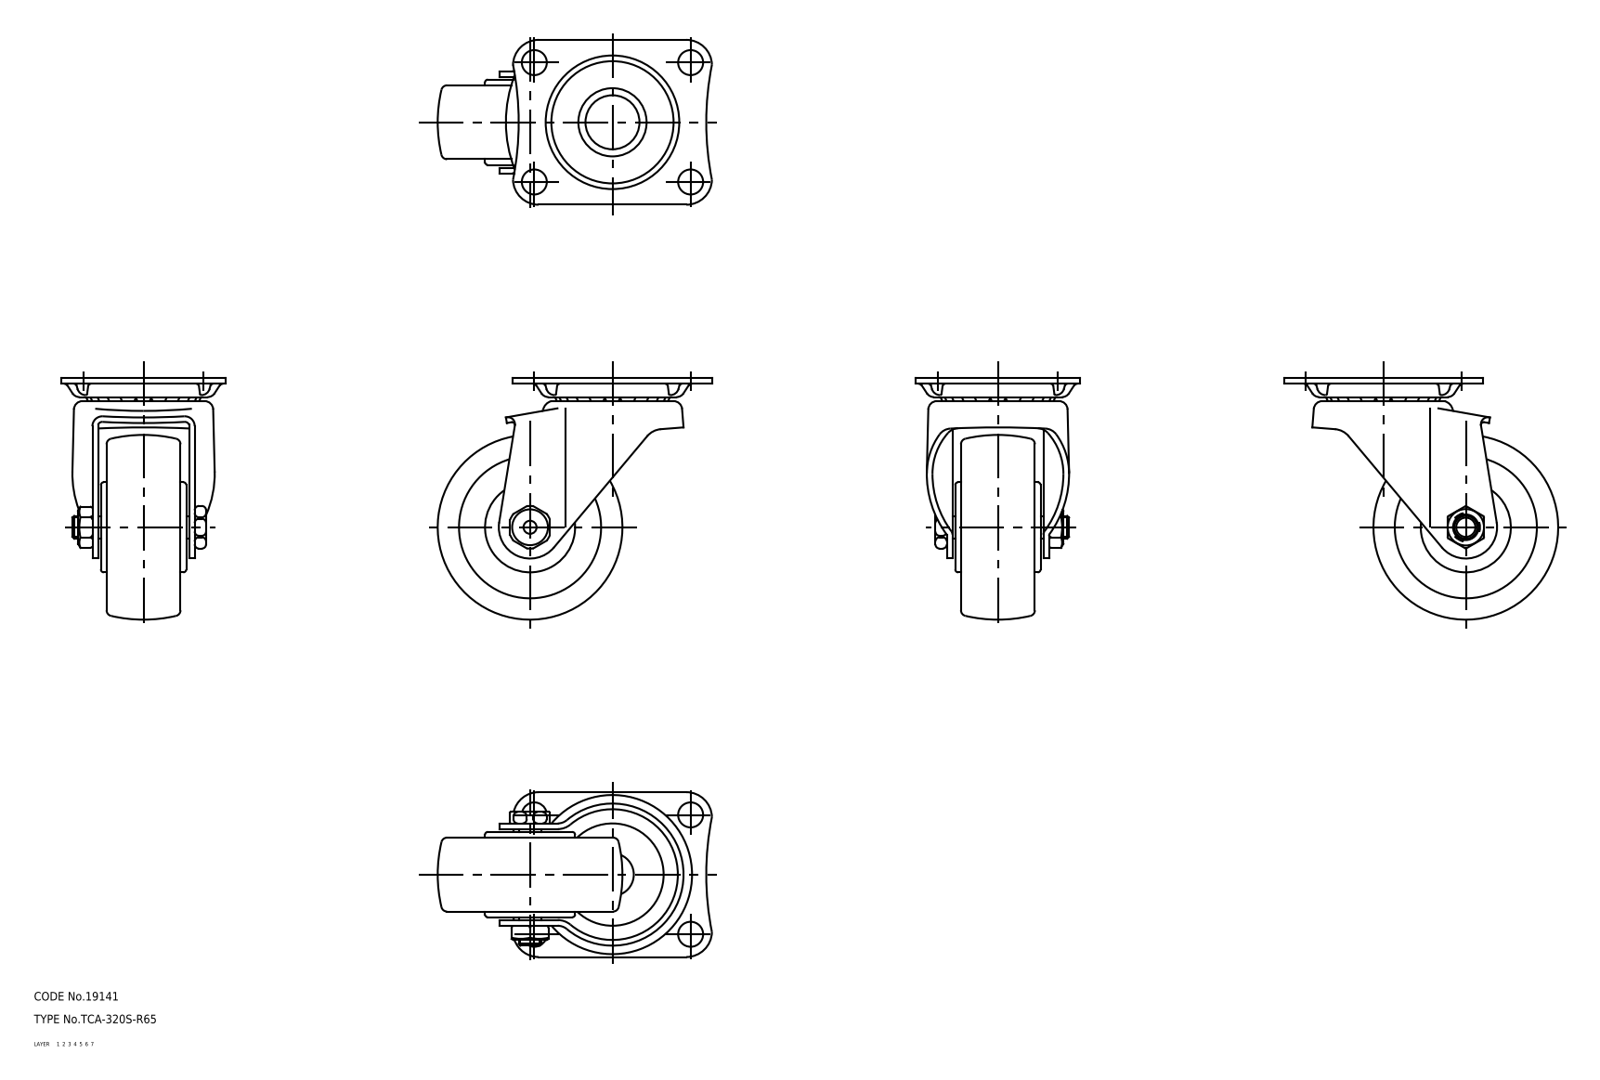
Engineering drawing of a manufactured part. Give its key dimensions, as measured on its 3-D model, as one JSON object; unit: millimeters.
{"part_name": "wheel; mounting plate; main shaft; axle (+1 more)", "step_written_by": "CADfix (AUTOMOTIVE_DESIGN)", "units": "millimeters", "bodies": {"solids": 5, "faces": 319, "planar": 0, "cylindrical": 0, "other": 319}, "overall_size": [96.5, 85, 58], "volume_mm3": 116836, "surface_area_mm2": 40556}
